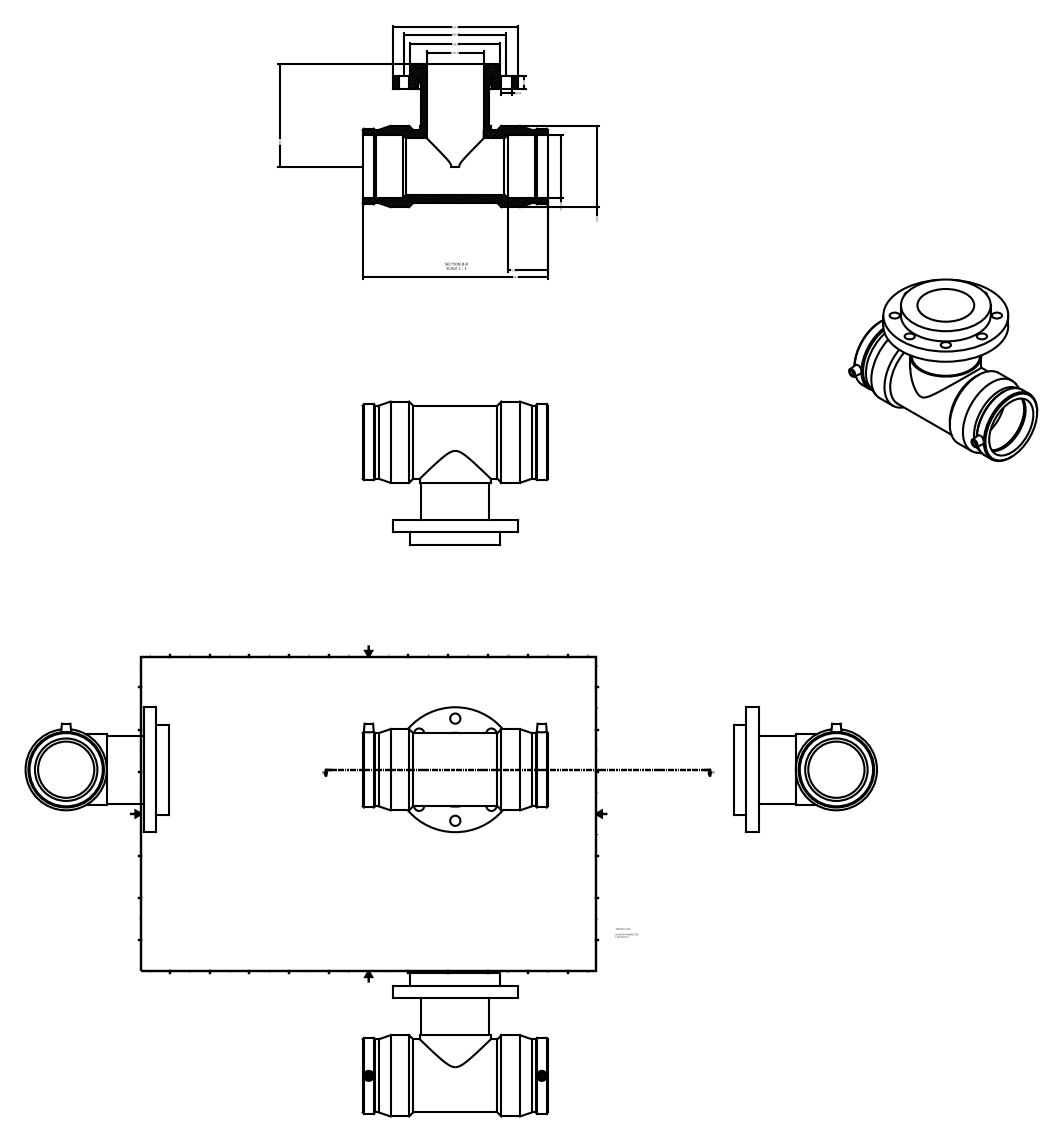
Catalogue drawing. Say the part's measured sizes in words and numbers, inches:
The part is named "499404110100". Its 3-D file was written by "Autodesk Inventor 2015 (AUTOMOTIVE_DESIGN)". It is 1 solid with 66 faces: 16 planar, 34 cylindrical and 16 other. Overall it measures 12.835 by 9.941 by 8.661 inches. Its volume is 172.9 cubic inches and its surface area 655.7 square inches. Round holes: 8 of diameter 0.709, 2 of diameter 0.394, 1 of diameter 3.898, 1 of diameter 3.937, 1 of diameter 4.331, 1 of diameter 5.118, 1 of diameter 5.236. Round bosses or shafts: 2 of diameter 0.157, 1 of diameter 8.661, 1 of diameter 6.22, 1 of diameter 5.63, 1 of diameter 5.079, 1 of diameter 5.067, 1 of diameter 4.921, 1 of diameter 4.724. The main face-to-face distances are 0.866, 1.732, 12.835, 4.311, 3.445, 2.579, 0.899, 11.936, 11.037, 0.551. The hole center spacings are 2.712, 3.543, 5.011, 6.547, 7.087, 11.996.
